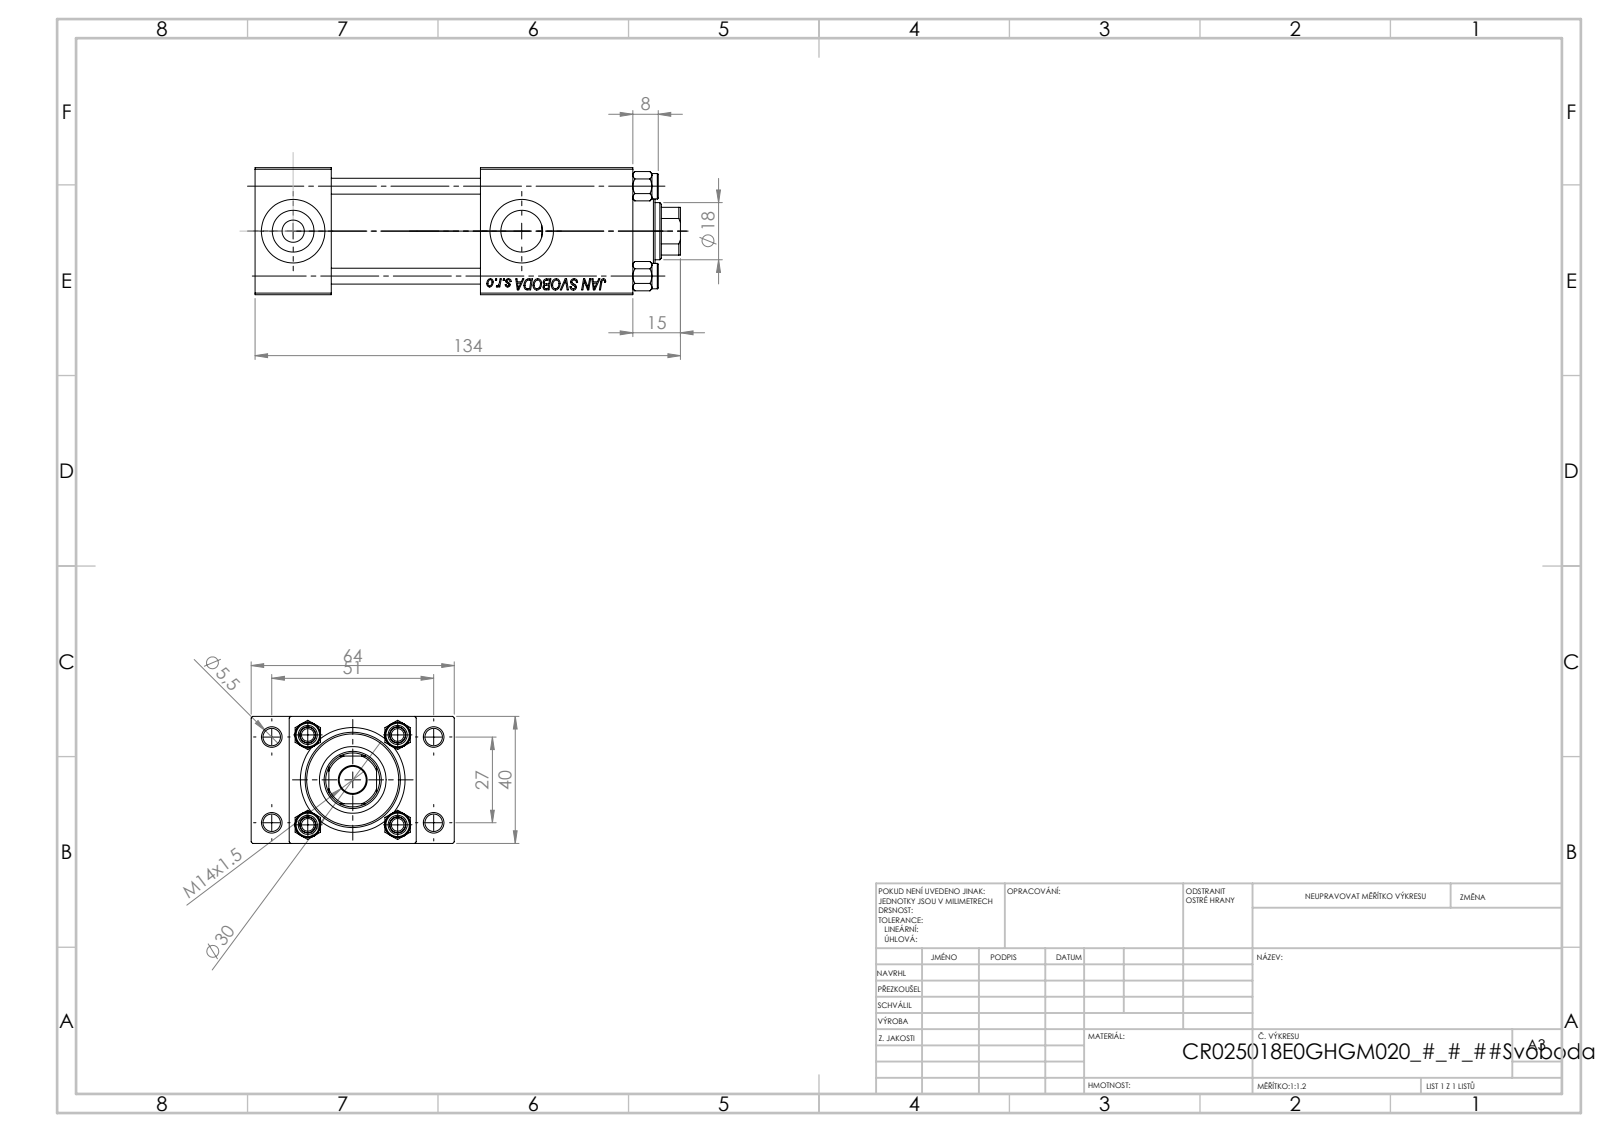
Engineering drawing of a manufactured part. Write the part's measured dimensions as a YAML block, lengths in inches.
part_name: "NUT_M5_E; V215CR_E_Body; V215_VC_A; V215CR_TYCINKA_E (+1 more)"
step_written_by: "SolidWorks 2019 (CONFIG_CONTROL_DESIGN)"
units: inches
bodies: {solids: 11, faces: 1132, planar: 496, cylindrical: 84, other: 552}
overall_size: [5.276, 2.52, 1.575]
volume: 10.44
surface_area: 100.2
round_holes:
  - {diameter: 0.197, count: 4}
  - {diameter: 0.217, count: 4}
  - {diameter: 0.787, count: 3}
  - {diameter: 0.276, count: 2}
  - {diameter: 0.518, count: 2}
  - {diameter: 0.335, count: 1}
  - {diameter: 0.709, count: 1}
  - {diameter: 0.827, count: 1}
  - {diameter: 0.984, count: 1}
  - {diameter: 1.181, count: 1}
round_bosses_or_shafts:
  - {diameter: 0.315, count: 4}
  - {diameter: 1.22, count: 1}
partial_cylinders:
  - {radius: 0.335, count: 1}
face_to_face_distances: [1.575, 0.945, 0.472, 2.047, 1.85, 2.795, 3.555, 2.61, 0.76, 4.685]
hole_center_spacings: [0.448, 0.788, 1.114, 1.136, 1.177, 1.561, 1.903, 1.063]
